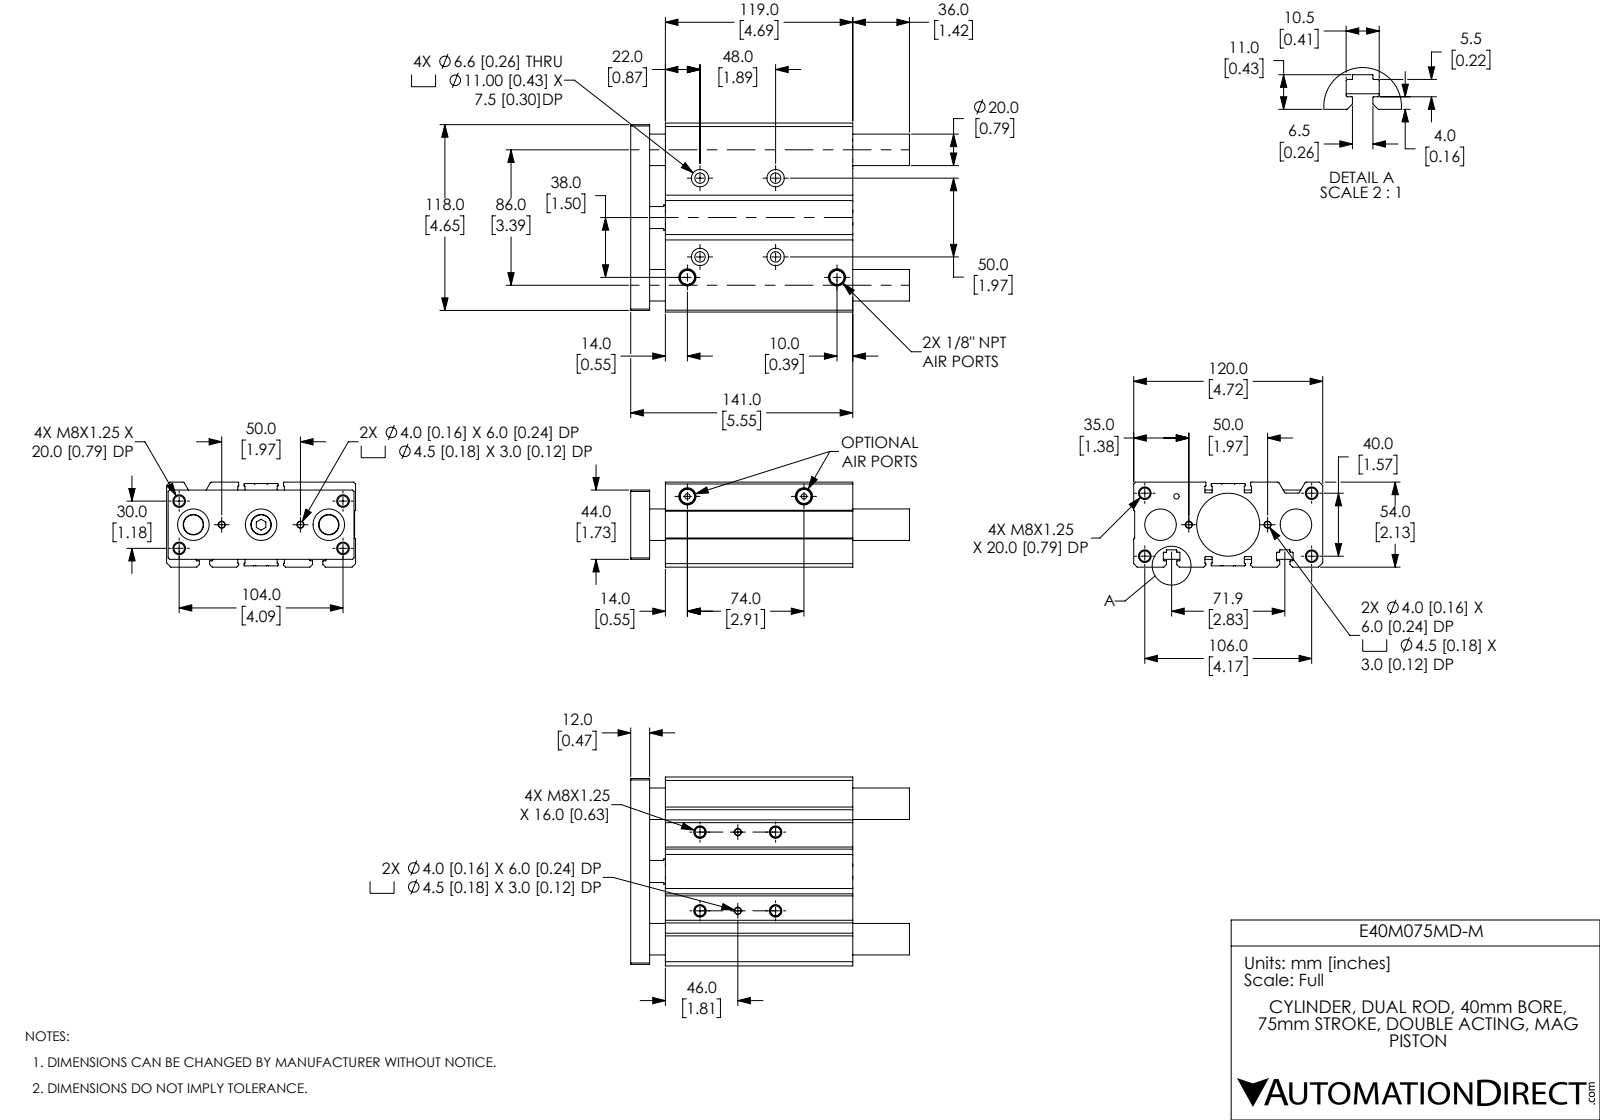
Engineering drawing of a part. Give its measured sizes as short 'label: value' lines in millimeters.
name: E40M075MD-M_BODY; E40M075MD-M_ENDPLATE; E40M075MD-M
written by: SolidWorks 2019 (CONFIG_CONTROL_DESIGN)
unit: mm
bodies: 5 solids, 427 faces (139 planar, 194 cylindrical, 94 other)
size: 177 × 120 × 54
volume: 708 333 mm³; area: 156 282 mm²
holes: 12× ⌀6.65, 4× ⌀4, 4× ⌀4.5, 4× ⌀6.6, 4× ⌀11, 3× ⌀3.43, 3× ⌀10, 3× ⌀20, 2× ⌀10.91, 2× ⌀12.95, 1× ⌀20, 1× ⌀40
bosses: 1× ⌀16, 1× ⌀12.95
rounds: 32× R0.2, 28× R0.4, 4× R1.2, 2× R0.3
face distances: 54, 119, 22, 12, 10, 141, 129, 120, 0.6, 4.15
hole spacings: 5.1, 17.49, 22.36, 24, 30.89, 34.41, 35.01, 50
